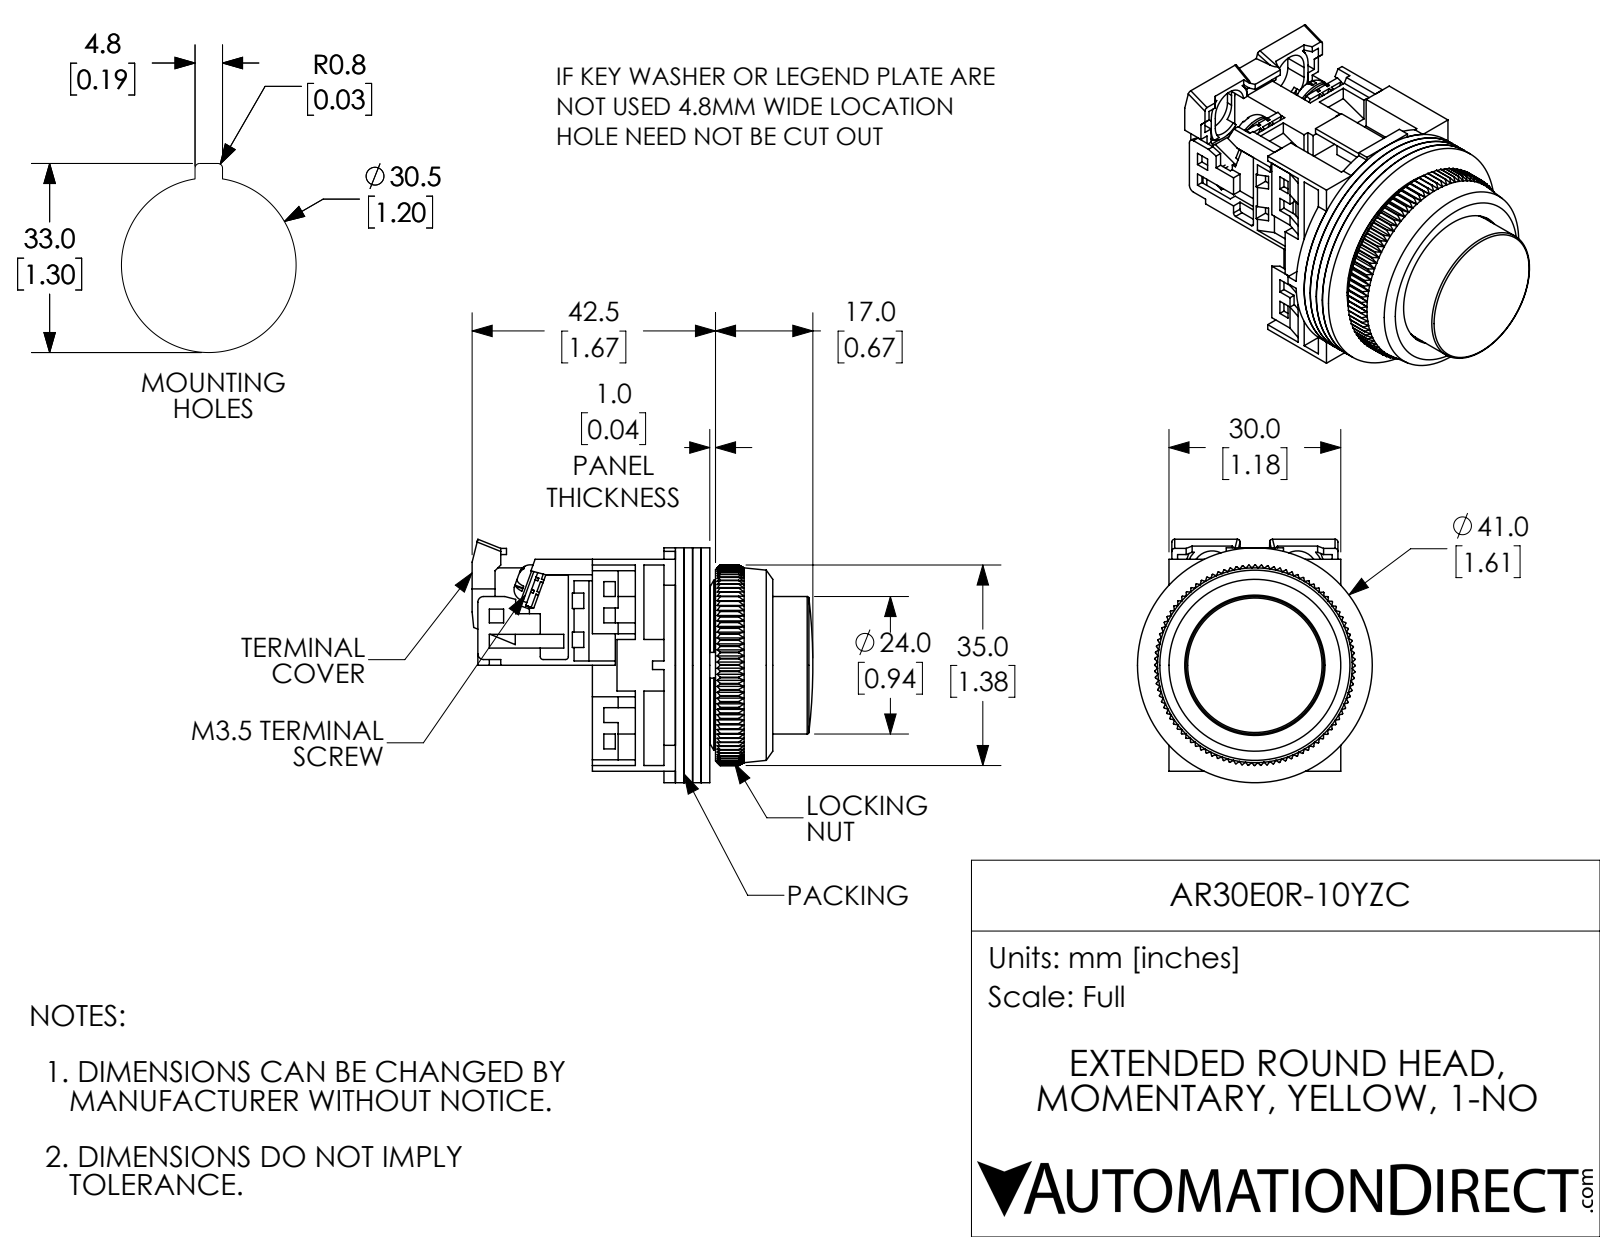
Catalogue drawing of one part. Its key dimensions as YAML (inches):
part_name: "AR30E0R-10YZC"
step_written_by: "SolidWorks 2017 (AUTOMOTIVE_DESIGN)"
units: inches
bodies: {solids: 16, faces: 1234, planar: 775, cylindrical: 249, other: 210}
overall_size: [2.342, 1.673, 1.614]
volume: 1.642
surface_area: 48.85
round_holes:
  - {diameter: 0.138, count: 4}
  - {diameter: 0.142, count: 2}
  - {diameter: 0.118, count: 1}
  - {diameter: 0.472, count: 1}
  - {diameter: 0.709, count: 1}
  - {diameter: 0.787, count: 1}
  - {diameter: 0.945, count: 1}
  - {diameter: 0.965, count: 1}
  - {diameter: 1.122, count: 1}
  - {diameter: 1.252, count: 1}
round_bosses_or_shafts:
  - {diameter: 0.26, count: 2}
  - {diameter: 0.138, count: 2}
  - {diameter: 1.614, count: 1}
  - {diameter: 1.181, count: 1}
  - {diameter: 0.866, count: 1}
  - {diameter: 0.551, count: 1}
partial_cylinders:
  - {radius: 0.059, count: 8}
  - {radius: 0.02, count: 6}
  - {radius: 0.039, count: 2}
  - {radius: 0.138, count: 2}
  - {radius: 0.177, count: 2}
  - {radius: 0.118, count: 1}
  - {radius: 0.398, count: 1}
  - {radius: 0.449, count: 1}
face_to_face_distances: [0.059, 0.118, 0.177, 0.039, 0.197, 0.079, 0.276, 0.689, 0.728, 0.602]
hole_center_spacings: [0.579, 0.61]
